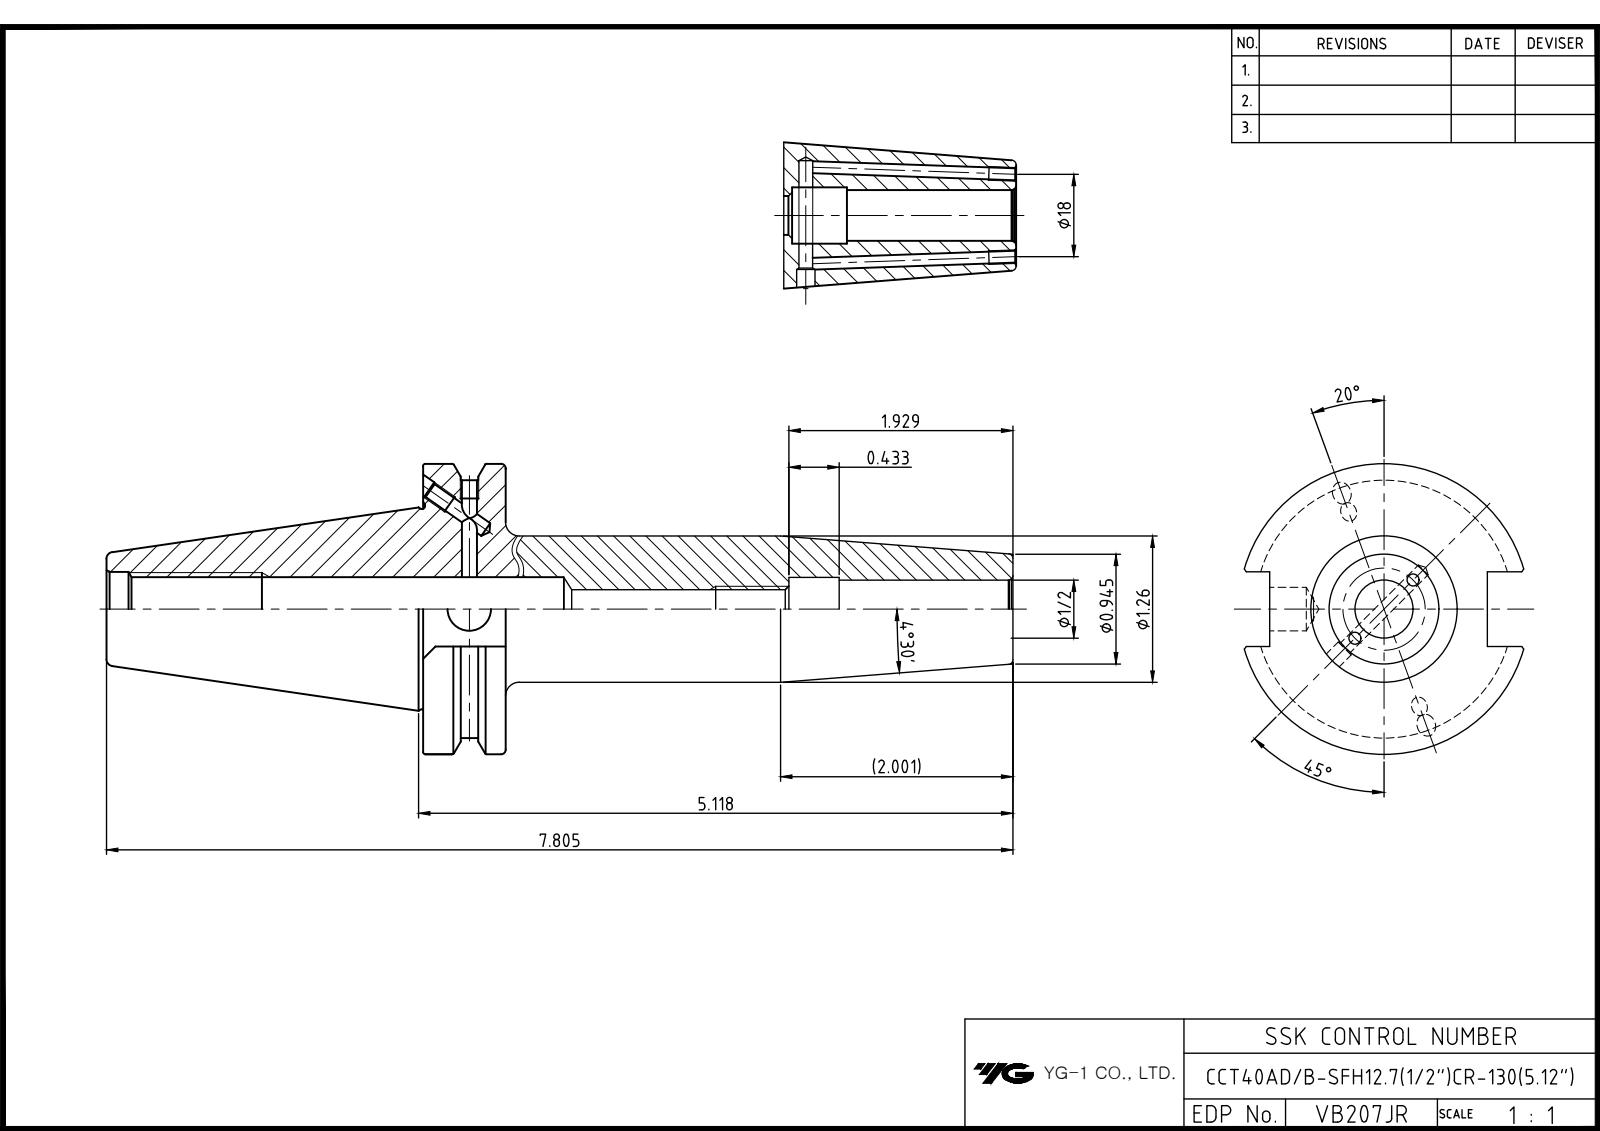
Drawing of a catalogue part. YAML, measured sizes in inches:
part_name: "LO-CCT40ADB-12.7CR-130"
step_written_by: "Autodesk Inventor 2022 (AUTOMOTIVE_DESIGN)"
units: inches
bodies: {solids: 1, faces: 89, planar: 38, cylindrical: 29, other: 22}
overall_size: [7.805, 2.5, 2.405]
volume: 10.42
surface_area: 54.81
round_holes:
  - {diameter: 0.128, count: 4}
  - {diameter: 0.157, count: 2}
  - {diameter: 0.165, count: 2}
  - {diameter: 0.351, count: 1}
  - {diameter: 0.375, count: 1}
  - {diameter: 0.5, count: 1}
  - {diameter: 0.512, count: 1}
  - {diameter: 0.527, count: 1}
  - {diameter: 0.547, count: 1}
  - {diameter: 0.642, count: 1}
round_bosses_or_shafts:
  - {diameter: 2.5, count: 1}
  - {diameter: 1.724, count: 1}
  - {diameter: 1.26, count: 1}
partial_cylinders:
  - {radius: 1.108, count: 1}
face_to_face_distances: [0.711, 5.079, 4.368, 1.874, 0.645, 2.726, 3.437, 7.805, 3.202, 0.476]
